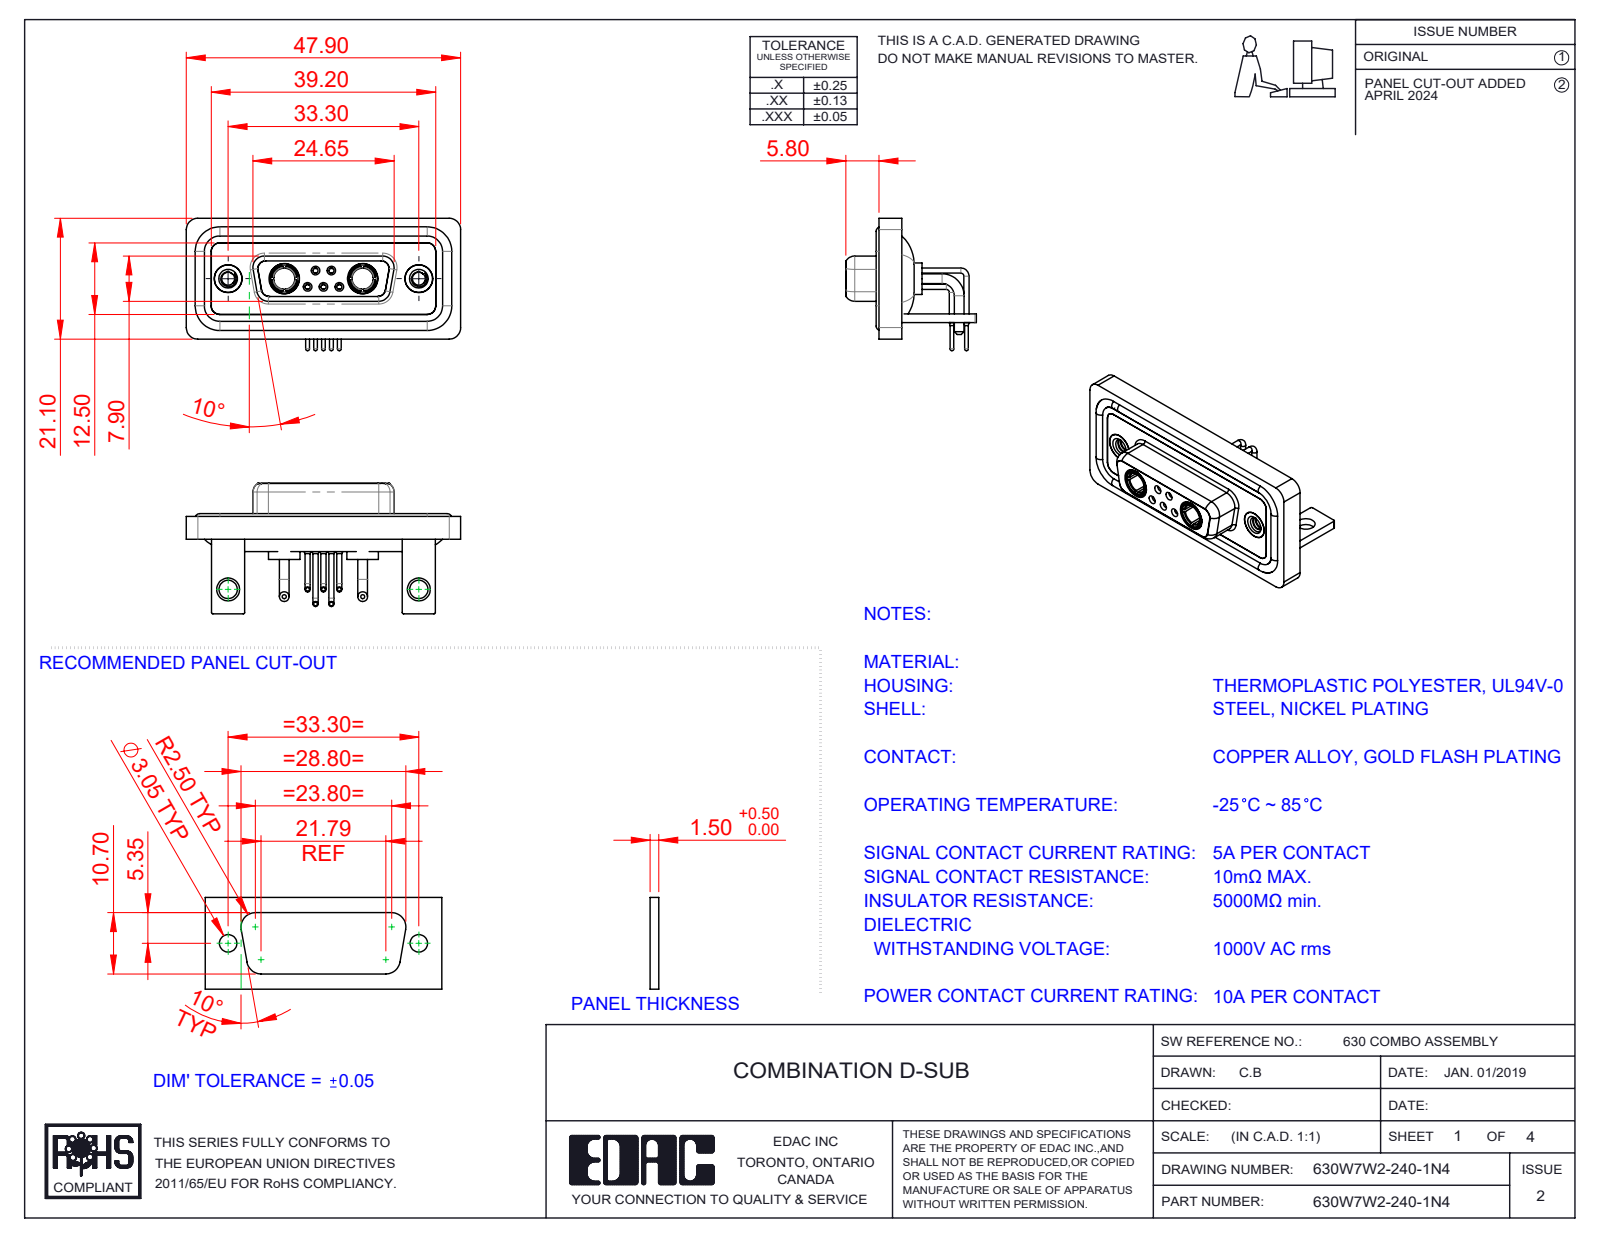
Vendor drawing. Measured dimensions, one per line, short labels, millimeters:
name: 630Combo Stabilizer Bracket_50 Contacts; Power Socket_10A RA; 630Combo Contact Row 2_50 Contacts; 630Combo Contact Row 1_50 Contacts (+6 more)
written by: SolidWorks 2023 (CONFIG_CONTROL_DESIGN)
unit: mm
bodies: 18 solids, 855 faces (258 planar, 377 cylindrical, 220 other)
size: 47.9 × 23.12 × 22.8
volume: 6 447 mm³; area: 10 839 mm²
holes: 5× ⌀0.9, 5× ⌀1.1, 5× ⌀1.5, 5× ⌀2, 4× ⌀4.85, 3× ⌀1.6, 2× ⌀1.7, 2× ⌀2.26, 2× ⌀3.2, 2× ⌀3.7, 2× ⌀4, 2× ⌀4.05
bosses: 6× ⌀1.6, 5× ⌀0.9, 5× ⌀0.65, 4× ⌀1.7, 2× ⌀5.5, 2× ⌀5.2, 2× ⌀4.96, 2× ⌀4.95
rounds: 21× R2, 18× R1.5, 16× R0.25, 12× R1.35, 8× R1.6, 5× R0.5, 4× R0.6, 4× R0.65
face distances: 0.4, 2.9, 1.5, 1.8, 3.7, 1.1, 4.1, 1.6, 2.5, 1.4
hole spacings: 3.16, 2.77, 9.8, 23.5, 33.3, 4.31, 4.33, 5.03
